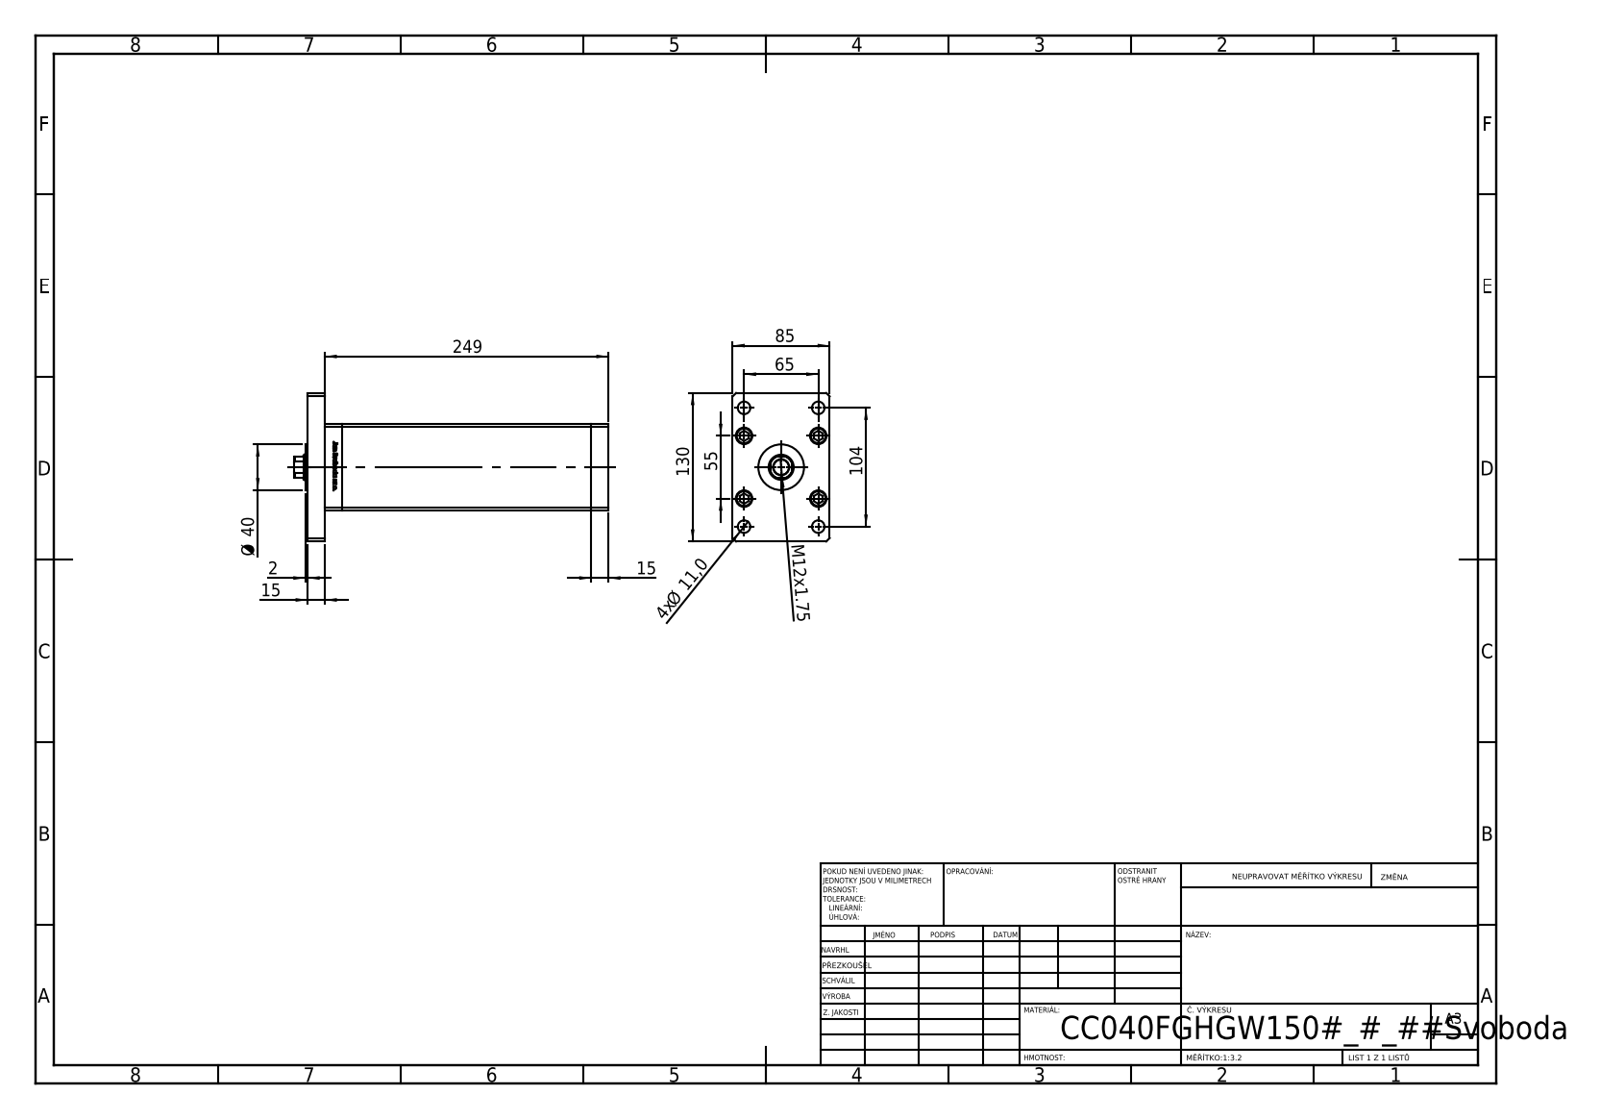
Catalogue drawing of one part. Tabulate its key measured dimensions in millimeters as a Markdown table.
| quantity | value |
| --- | --- |
| part name | V220C BACK_F; ALLEN BOLT; V220C_VC_F; V220C_F (+2 more) |
| STEP written by | SolidWorks 2019 (CONFIG_CONTROL_DESIGN) |
| units | millimeters |
| bodies | 19 solids, 1308 faces (515 planar, 187 cylindrical, 606 other) |
| overall size | 275 × 130 × 85 |
| volume | 1 536 000 mm³ |
| surface area | 236 256 mm² |
| round holes (diameter × count) | 11 × 9, 15.5 × 5, 10 × 4, 14.5 × 4, 2 × 2, 13.16 × 2, 13.5 × 1, 22 × 1, 23.5 × 1 |
| round bosses / shafts (diameter × count) | 8 × 9, 14.5 × 5, 40 × 1 |
| partial cylindrical surfaces (radius × count) | 0.93 × 2, 10.5 × 1 |
| main face-to-face distances | 15, 85, 75, 233.5, 248.5, 218.5, 30, 263.5, 10.5, 27.5 |
| hole center spacings | 28, 24.5, 42.57, 61.32, 65, 69.46, 79.5, 102.69 |
